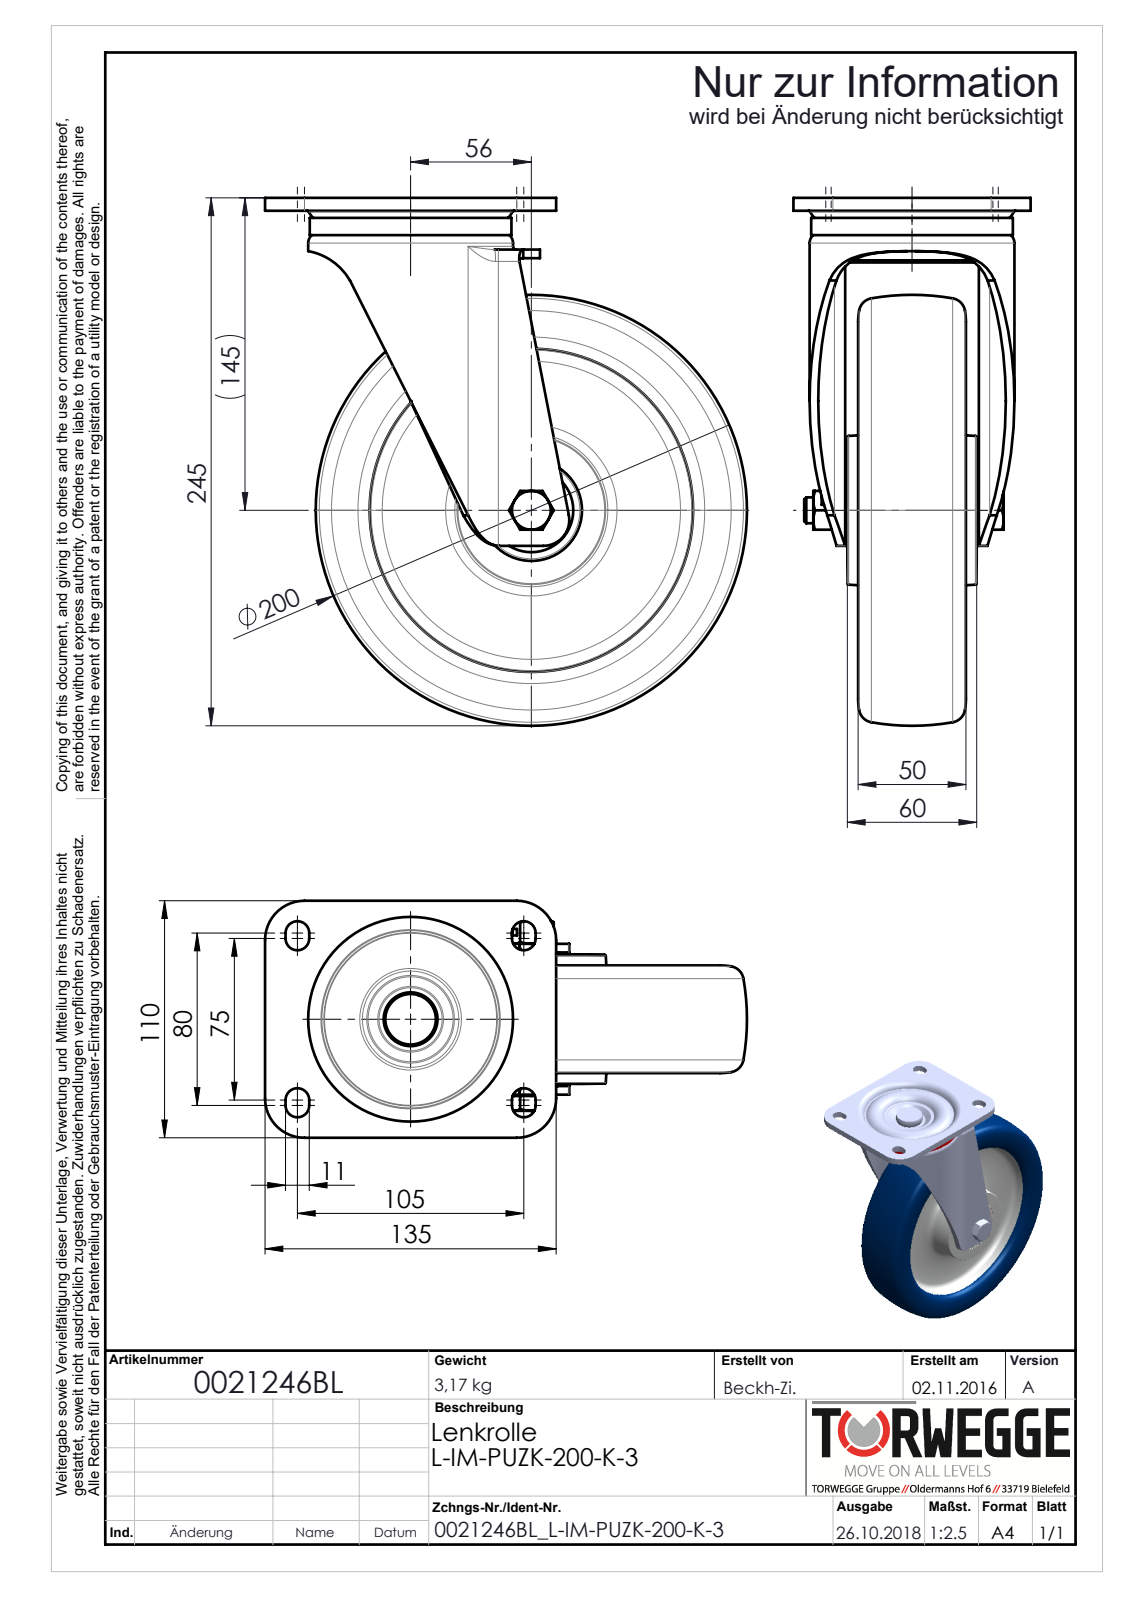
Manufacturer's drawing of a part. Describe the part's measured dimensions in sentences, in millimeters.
The part is named "0021246_L-IM-PUZK-200-K-3". Its 3-D file was written by "SolidWorks 2016 (AUTOMOTIVE_DESIGN)". It is 0 solids with 498 faces: 227 planar, 108 cylindrical and 163 other. Overall it measures 245 by 223.5 by 110 millimeters. Round holes: 1 of diameter 10.2, 1 of diameter 12, 1 of diameter 12.2, 1 of diameter 20, 1 of diameter 35, 1 of diameter 38.9, 1 of diameter 87. Round bosses or shafts: 1 of diameter 95, 1 of diameter 93.54, 1 of diameter 61.97, 1 of diameter 28.1, 1 of diameter 25, 1 of diameter 19.9, 1 of diameter 18. Partial cylindrical surfaces (rounded edges, fillets, slot ends): 10 of radius 5.5, 5 of radius 0.62, 4 of radius 0.86, 4 of radius 18.29, 3 of radius 0.21, 3 of radius 0.37, 3 of radius 0.93, 2 of radius 0.67. The main face-to-face distances are 6, 4, 66, 62, 24, 70, 1, 20, 5, 1.5.
